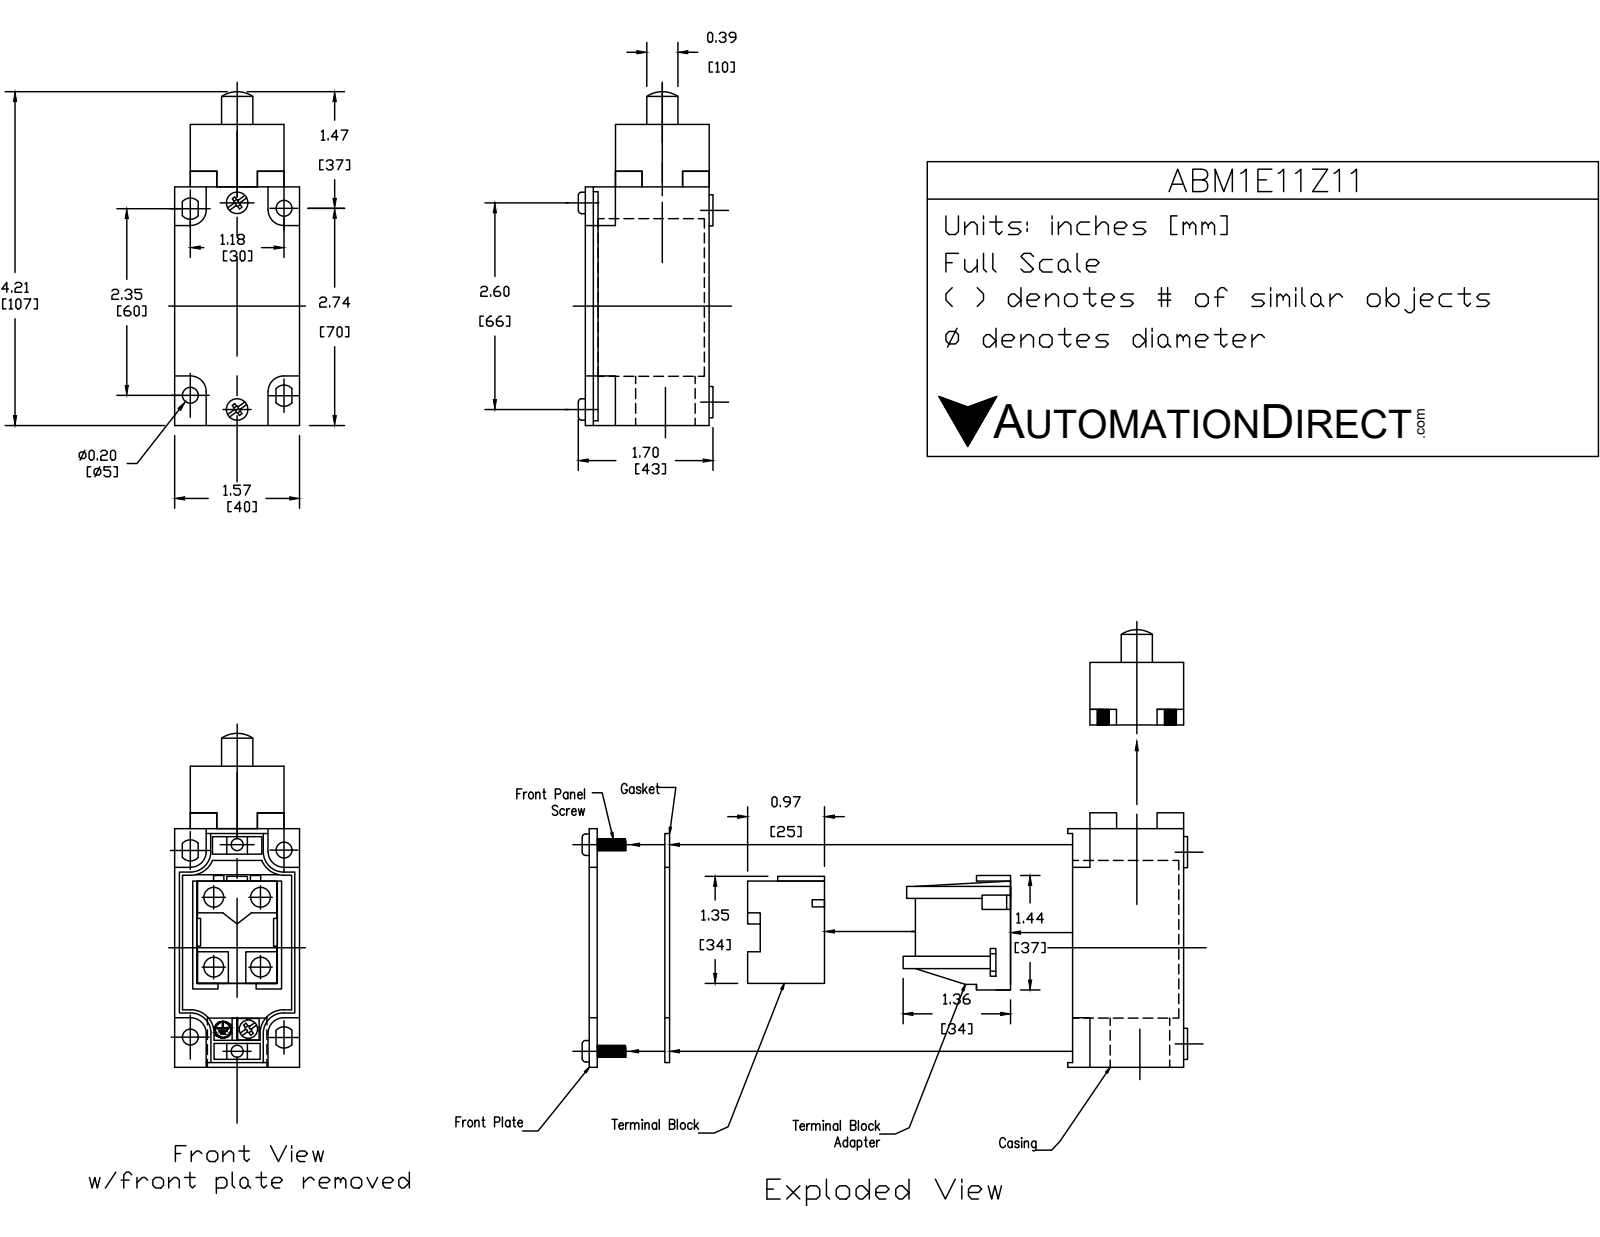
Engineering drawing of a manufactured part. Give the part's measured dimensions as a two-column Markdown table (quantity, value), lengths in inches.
| quantity | value |
| --- | --- |
| part name | ABM1E11Z11 |
| STEP written by | SolidWorks 2017 (AUTOMOTIVE_DESIGN) |
| units | inches |
| bodies | 3 solids, 151 faces (68 planar, 66 cylindrical, 17 other) |
| overall size | 4.196 × 1.705 × 1.575 |
| volume | 7.787 in³ |
| surface area | 37.63 in² |
| round holes (diameter × count) | 0.205 × 2, 0.394 × 1, 0.669 × 1, 0.748 × 1 |
| round bosses / shafts (diameter × count) | 0.394 × 4, 0.276 × 2 |
| partial cylindrical surfaces (radius × count) | 0.059 × 16, 0.039 × 4, 0.197 × 4, 0.128 × 2, 0.453 × 1, 0.472 × 1 |
| main face-to-face distances | 1.575, 1.555, 1.181, 0.197, 1.378, 0.374, 3.012, 3.209, 0.591, 3.031 |
| hole center spacings | 0.039, 2.641 |
